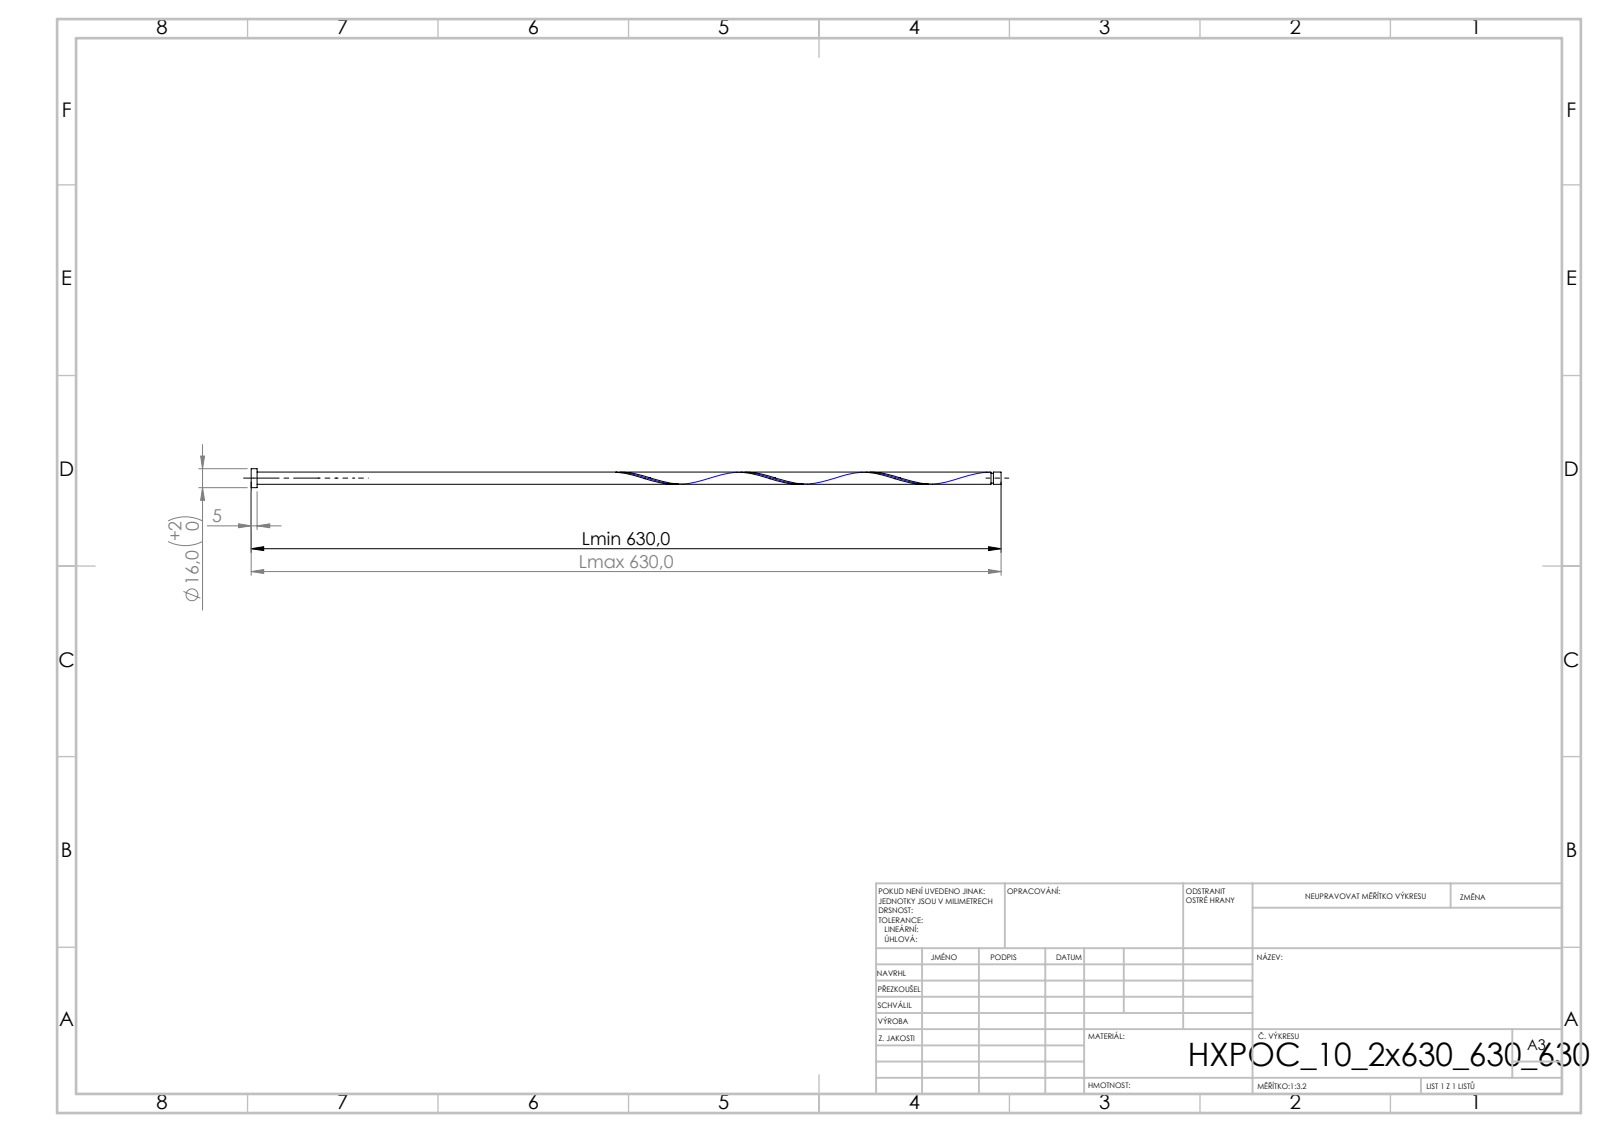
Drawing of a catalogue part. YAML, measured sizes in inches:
step_written_by: "SolidWorks 2019 (CONFIG_CONTROL_DESIGN)"
units: inches
bodies: {solids: 1, faces: 16, planar: 6, cylindrical: 9, other: 1}
overall_size: [24.803, 0.63, 0.63]
volume: 3.842
surface_area: 43.05
round_bosses_or_shafts:
  - {diameter: 0.63, count: 1}
  - {diameter: 0.402, count: 1}
  - {diameter: 0.321, count: 1}
face_to_face_distances: [0.197, 24.803, 24.606, 24.548, 24.351, 0.255, 24.468, 24.271, 0.08, 0.335]
